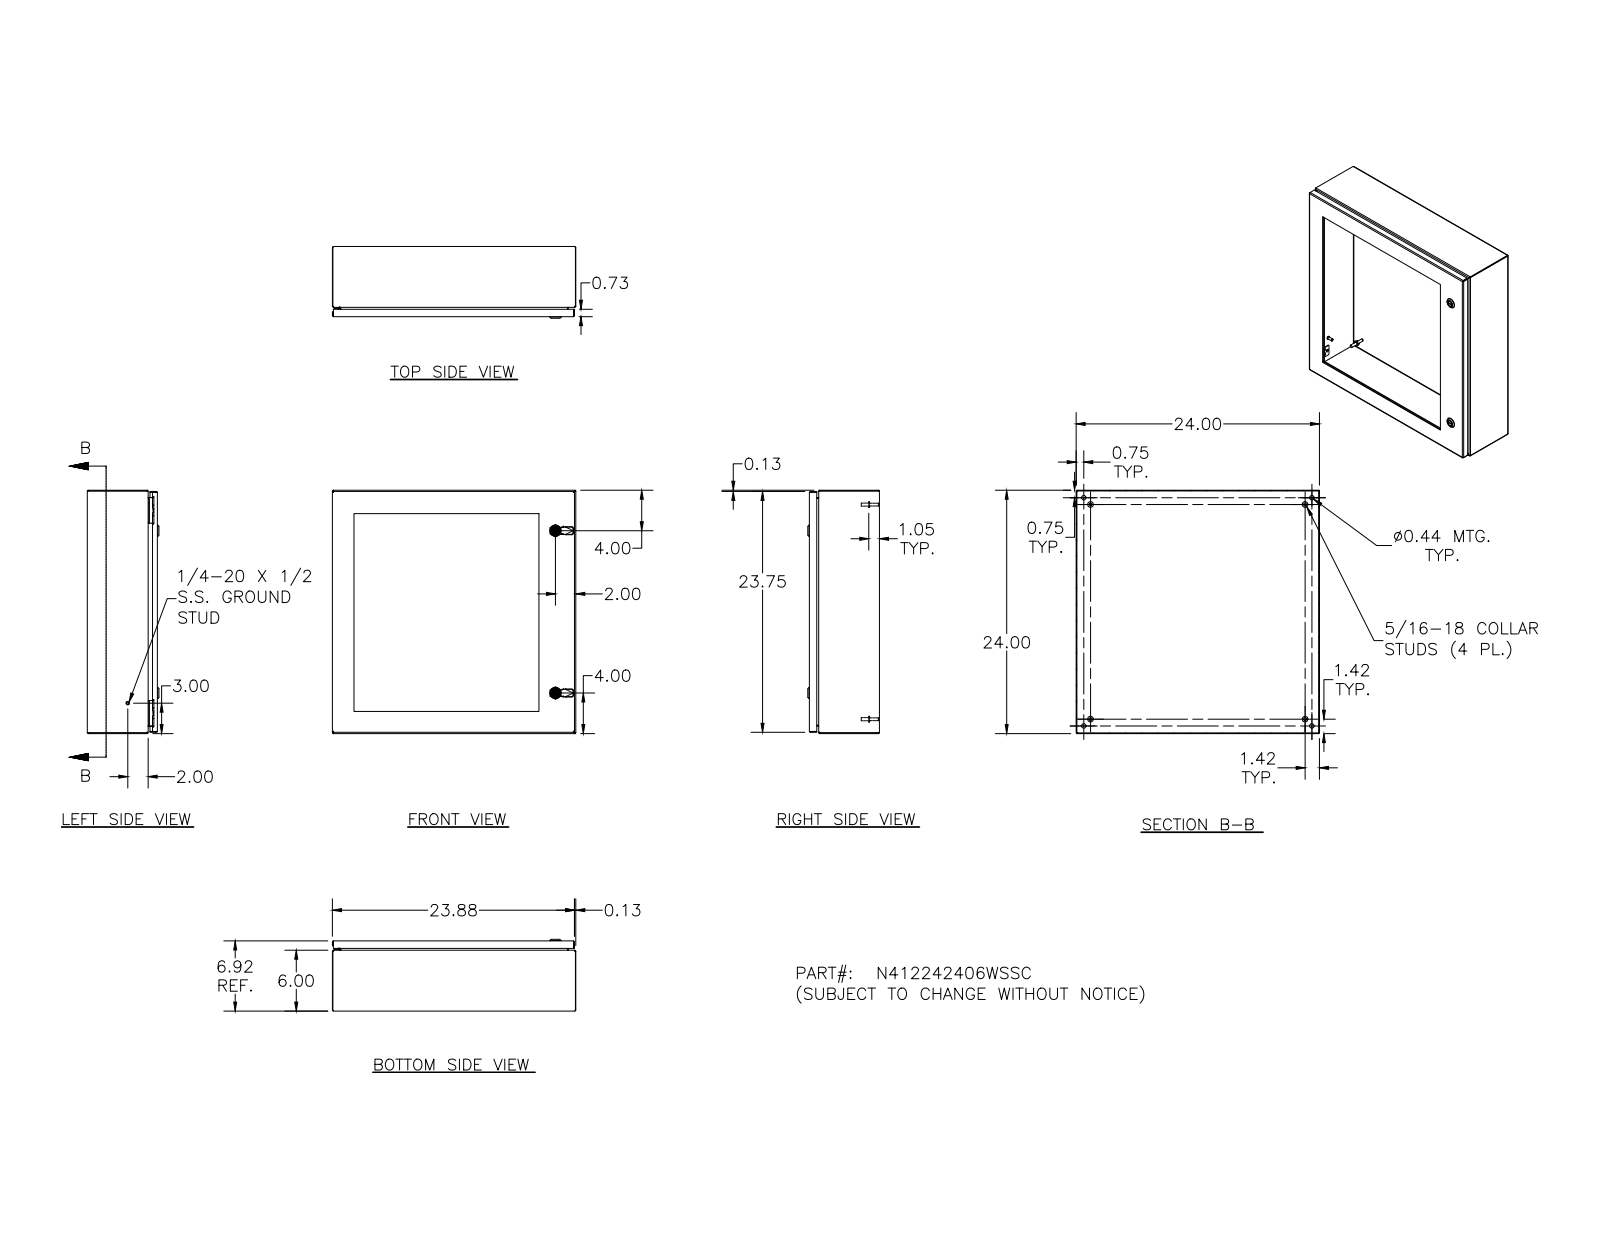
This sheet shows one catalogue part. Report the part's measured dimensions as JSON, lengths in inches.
{"part_name": "N412242406WSSC; N412242406WSSCBKP; N4122424WSSCLID; HFW328176 (+8 more)", "step_written_by": "Autodesk Inventor 2011 (AUTOMOTIVE_DESIGN)", "units": "inches", "bodies": {"solids": 86, "faces": 2366, "planar": 973, "cylindrical": 672, "other": 721}, "overall_size": [24, 24, 7.075], "volume_in3": 221.9, "surface_area_in2": 4176, "round_holes": [[0.156, 22], [0.281, 20], [0.093, 4], [0.152, 4], [0.167, 4], [0.172, 4], [0.188, 4], [0.437, 4], [0.197, 2], [0.315, 2], [0.394, 2], [0.402, 2]], "round_bosses_or_shafts": [[0.19, 20], [0.253, 19], [0.25, 10], [0.563, 4], [0.36, 4], [0.32, 4], [0.3, 4], [0.275, 4]], "partial_cylinders_radius": [[0.031, 34], [0.05, 26], [0.105, 24], [0.016, 18], [0.125, 16], [0.02, 15], [0.032, 8], [0.157, 8]], "face_to_face_distances": [0.074, 6.843, 6.769, 23.926, 0.25, 6.593, 6.519, 23.852, 24, 6.917], "hole_center_spacings": [4, 8, 21.132, 12, 19.906, 20, 22.239, 20.75]}
